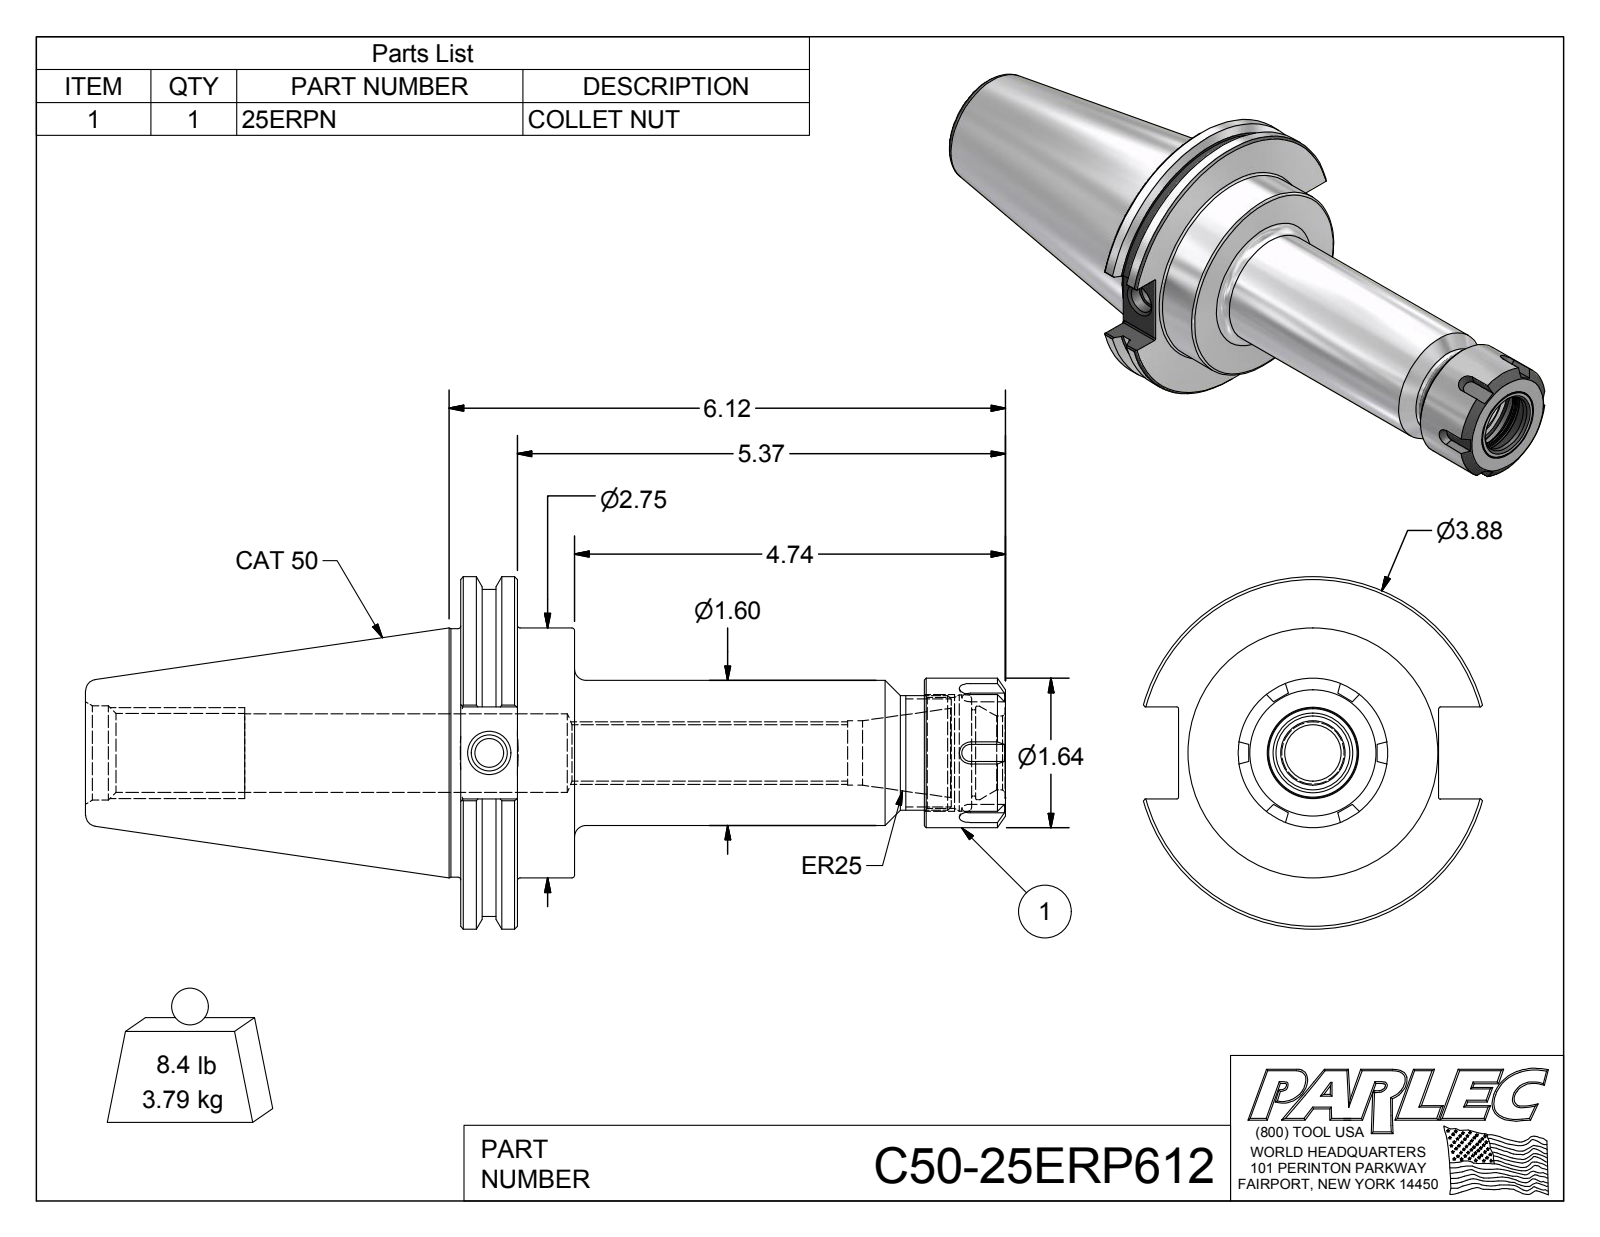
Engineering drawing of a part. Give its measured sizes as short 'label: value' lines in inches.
name: C50-25ERP612; C50-25ER6-1; 25ERPN
written by: Autodesk Inventor 2012 (AUTOMOTIVE_DESIGN)
unit: in
bodies: 2 solids, 127 faces (52 planar, 31 cylindrical, 44 other)
size: 10.12 × 3.875 × 3.729
volume: 29.98 in³; area: 114.1 in²
holes: 1× ⌀0.315, 1× ⌀0.399, 1× ⌀0.62, 1× ⌀0.71, 1× ⌀0.811, 1× ⌀0.864, 1× ⌀0.865, 1× ⌀0.95, 1× ⌀1.027, 1× ⌀1.038, 1× ⌀1.217, 1× ⌀1.28
bosses: 1× ⌀3.875, 1× ⌀3.594, 1× ⌀2.75, 1× ⌀2.73, 1× ⌀1.643, 1× ⌀1.595, 1× ⌀1.26
rounds: 8× R0.02
face distances: 0.625, 1.255, 0.63, 5.995, 5.37, 4.74, 5.102, 4.477, 3.847, 0.893
